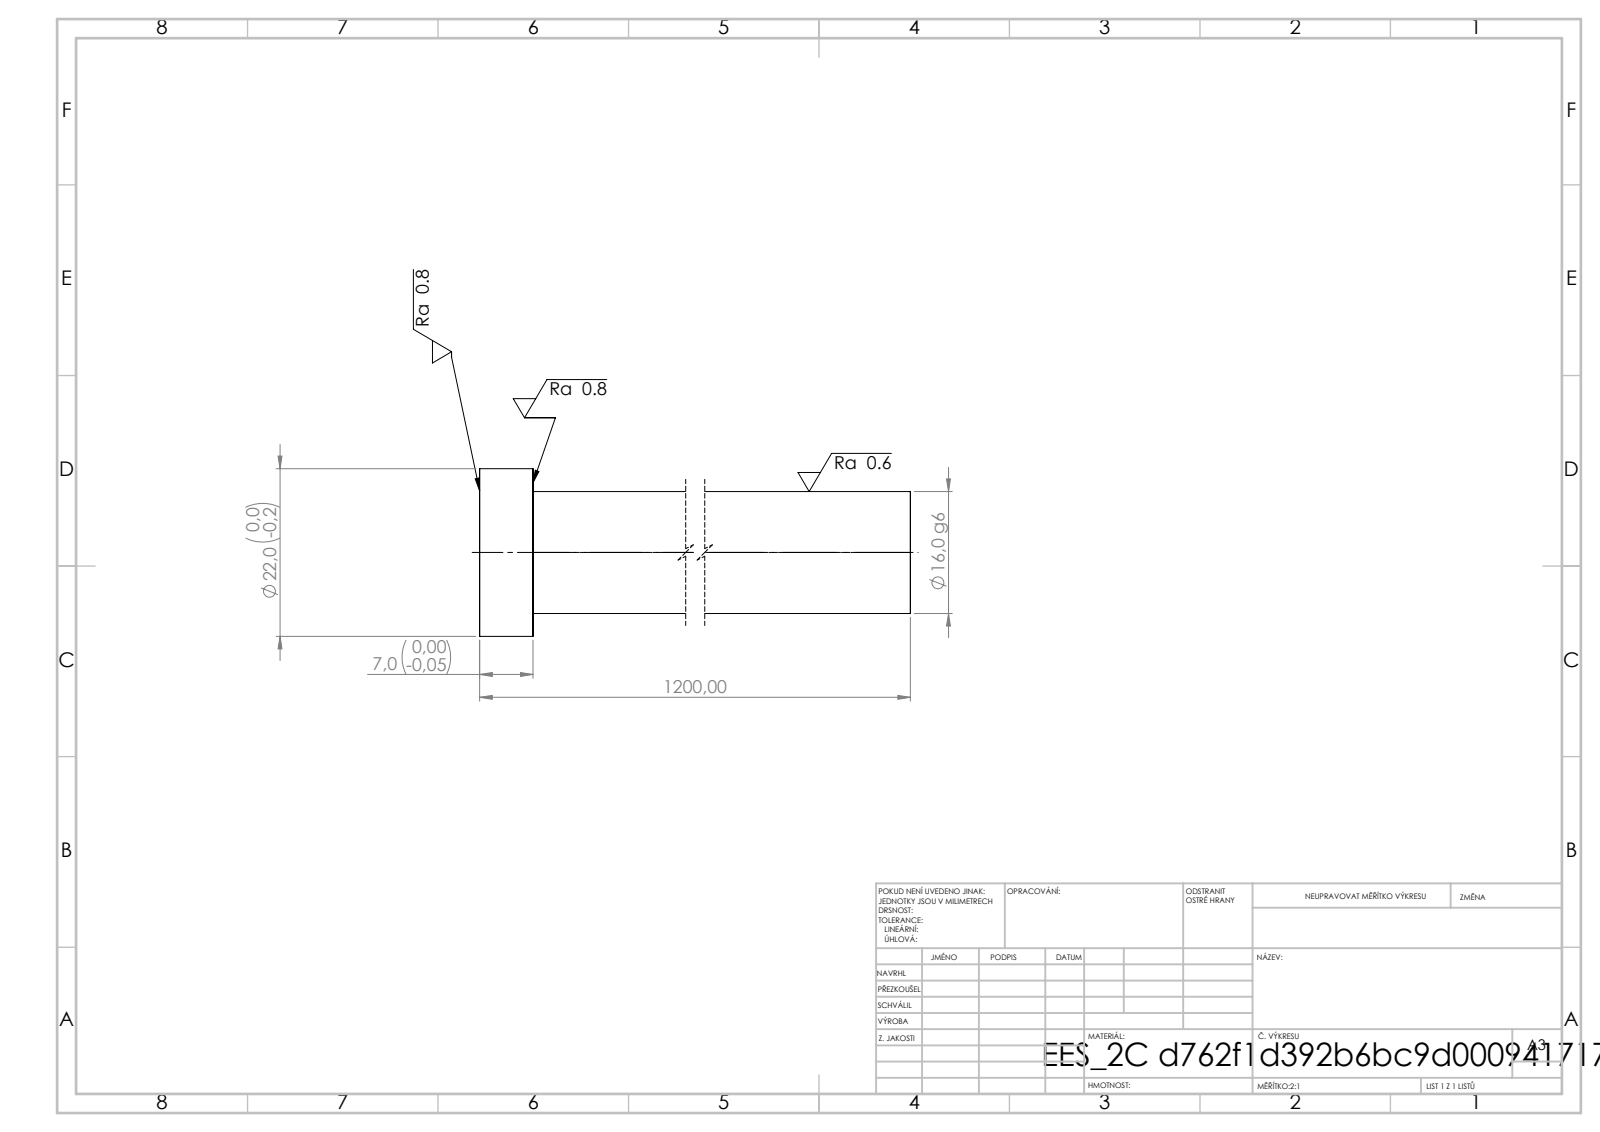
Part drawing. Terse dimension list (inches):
written by: SolidWorks 2019 (CONFIG_CONTROL_DESIGN)
unit: in
bodies: 1 solid, 7 faces (3 planar, 4 cylindrical, 0 other)
size: 47.244 × 0.866 × 0.866
volume: 14.8 in³; area: 94.88 in²
bosses: 1× ⌀0.866, 1× ⌀0.63
face distances: 47.244, 0.276, 46.969
